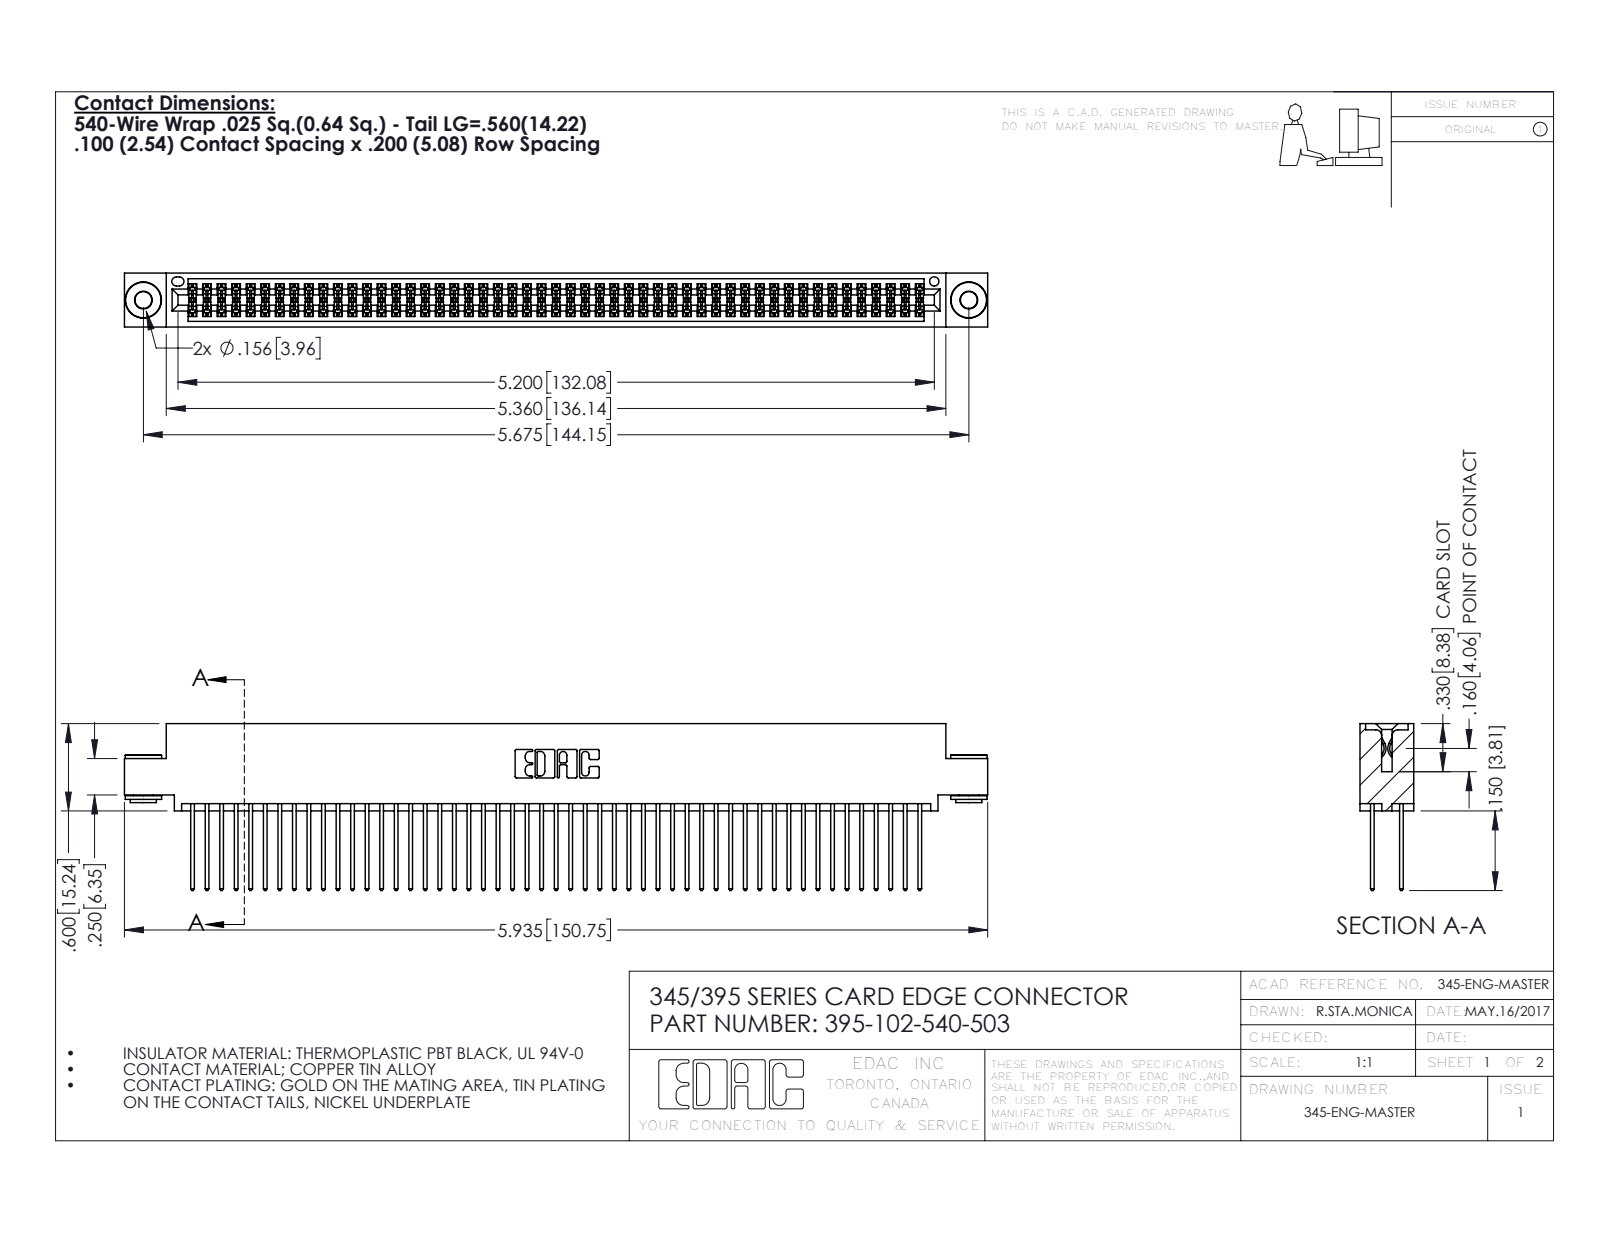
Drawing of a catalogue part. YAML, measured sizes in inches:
part_name: "345 Part_0.110 Offset - 0.156 Dia-TH; 345-250-002_345-250-002-102; 395-102-540-503; 345-292-001_345-293-140"
step_written_by: "SolidWorks 2016 (CONFIG_CONTROL_DESIGN)"
units: inches
bodies: {solids: 105, faces: 5268, planar: 3460, cylindrical: 1800, other: 8}
overall_size: [5.935, 1.147, 0.37]
volume: 0.919
surface_area: 38.02
round_holes:
  - {diameter: 0.116, count: 2}
  - {diameter: 0.156, count: 2}
  - {diameter: 0.064, count: 1}
round_bosses_or_shafts:
  - {diameter: 0.25, count: 2}
  - {diameter: 0.18, count: 2}
  - {diameter: 0.136, count: 2}
partial_cylinders:
  - {radius: 0.006, count: 153}
  - {radius: 0.01, count: 102}
  - {radius: 0.01, count: 22}
  - {radius: 0.007, count: 6}
  - {radius: 0.031, count: 6}
  - {radius: 0.026, count: 3}
  - {radius: 0.014, count: 2}
  - {radius: 0.019, count: 2}
face_to_face_distances: [0.072, 0.298, 0.2, 0.025, 0.098, 0.272, 0.37, 0.225, 0.175, 0.149]
hole_center_spacings: [0.27, 5.439, 5.675]
